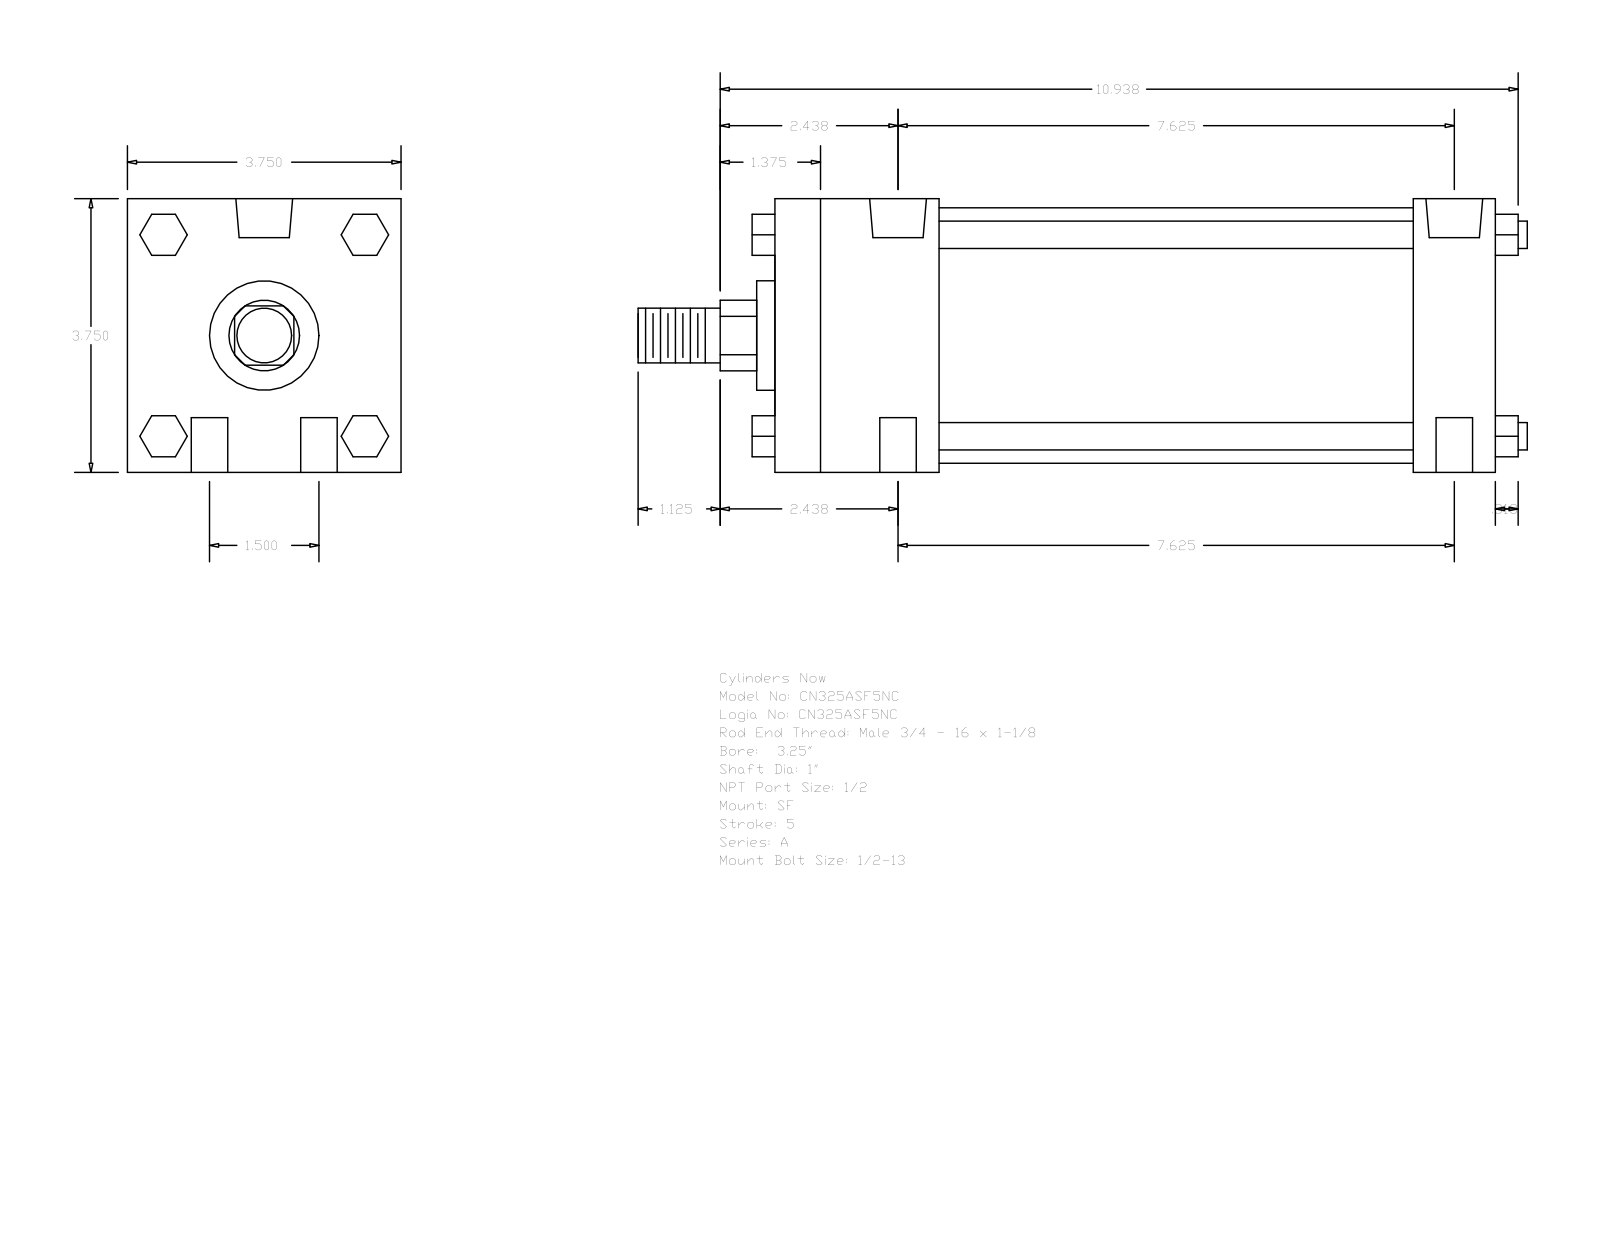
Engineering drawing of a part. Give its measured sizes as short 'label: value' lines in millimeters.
name: A_SF__0325_1
written by: GSSL Pune (CONFIG_CONTROL_DESIGN)
unit: mm
bodies: 0 solids, 124 faces (94 planar, 30 cylindrical, 0 other)
size: 309.56 × 95.25 × 95.25
holes: 4× ⌀12.7, 2× ⌀8.73, 2× ⌀19.77
bosses: 4× ⌀9.53, 1× ⌀88.9, 1× ⌀38.1, 1× ⌀25.4, 1× ⌀19.05
rounds: 1× R12.29
face distances: 95.24, 250.83, 222.25, 28.58, 57.15, 165.1, 193.68, 14.28, 35.05, 60.71
hole spacings: 19.05, 194.61, 193.68, 38.1, 197.39, 187.32
